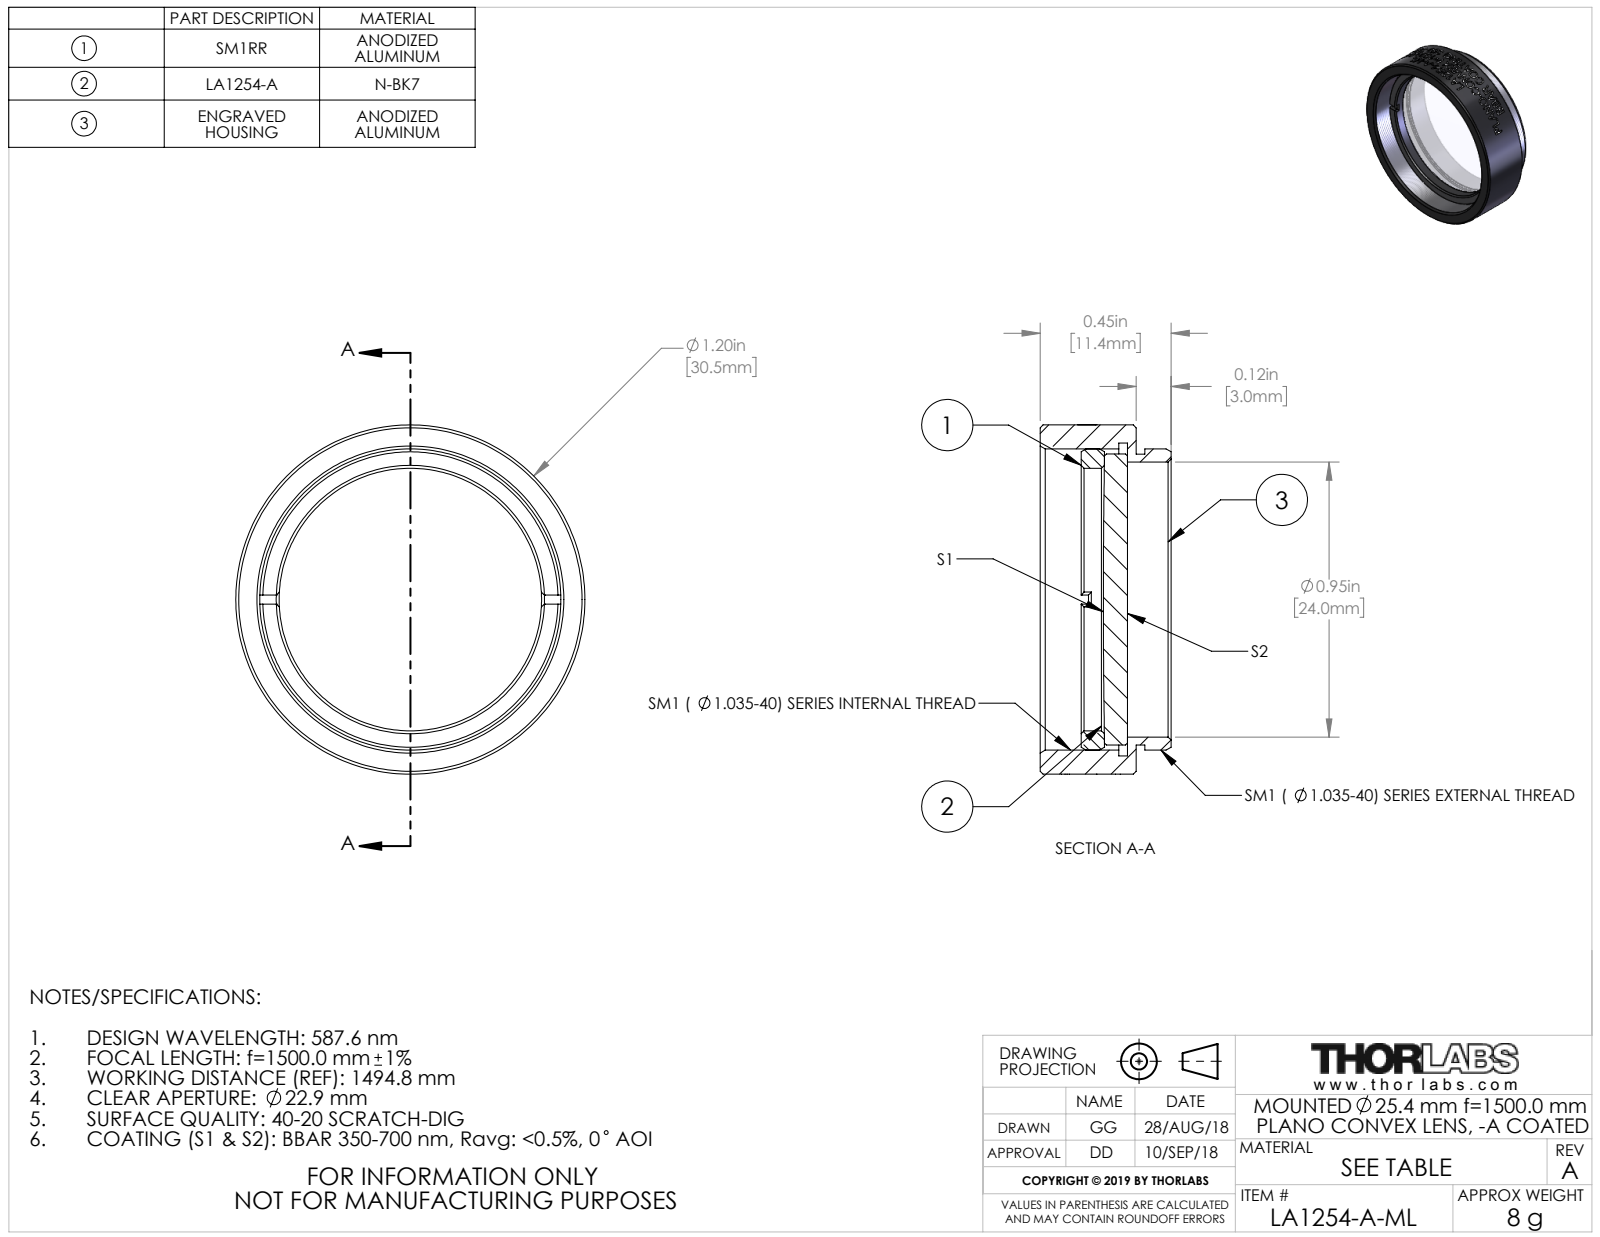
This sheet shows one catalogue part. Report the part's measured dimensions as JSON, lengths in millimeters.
{"part_name": "TTN162135-E0W", "step_written_by": "SolidWorks 2018 (CONFIG_CONTROL_DESIGN)", "units": "millimeters", "bodies": {"solids": 3, "faces": 177, "planar": 20, "cylindrical": 129, "other": 28}, "overall_size": [30.48, 30.48, 11.43], "volume_mm3": 3116, "surface_area_mm2": 4296, "round_holes": [[22.91, 1], [24, 1], [27.3, 1]], "round_bosses_or_shafts": [[30.48, 1], [26.29, 1], [25.4, 1], [25.37, 1]], "face_to_face_distances": [0.77, 8.39, 7.62, 2.78, 2.01, 5.61, 4.81, 4.04, 2.03, 3.58]}
